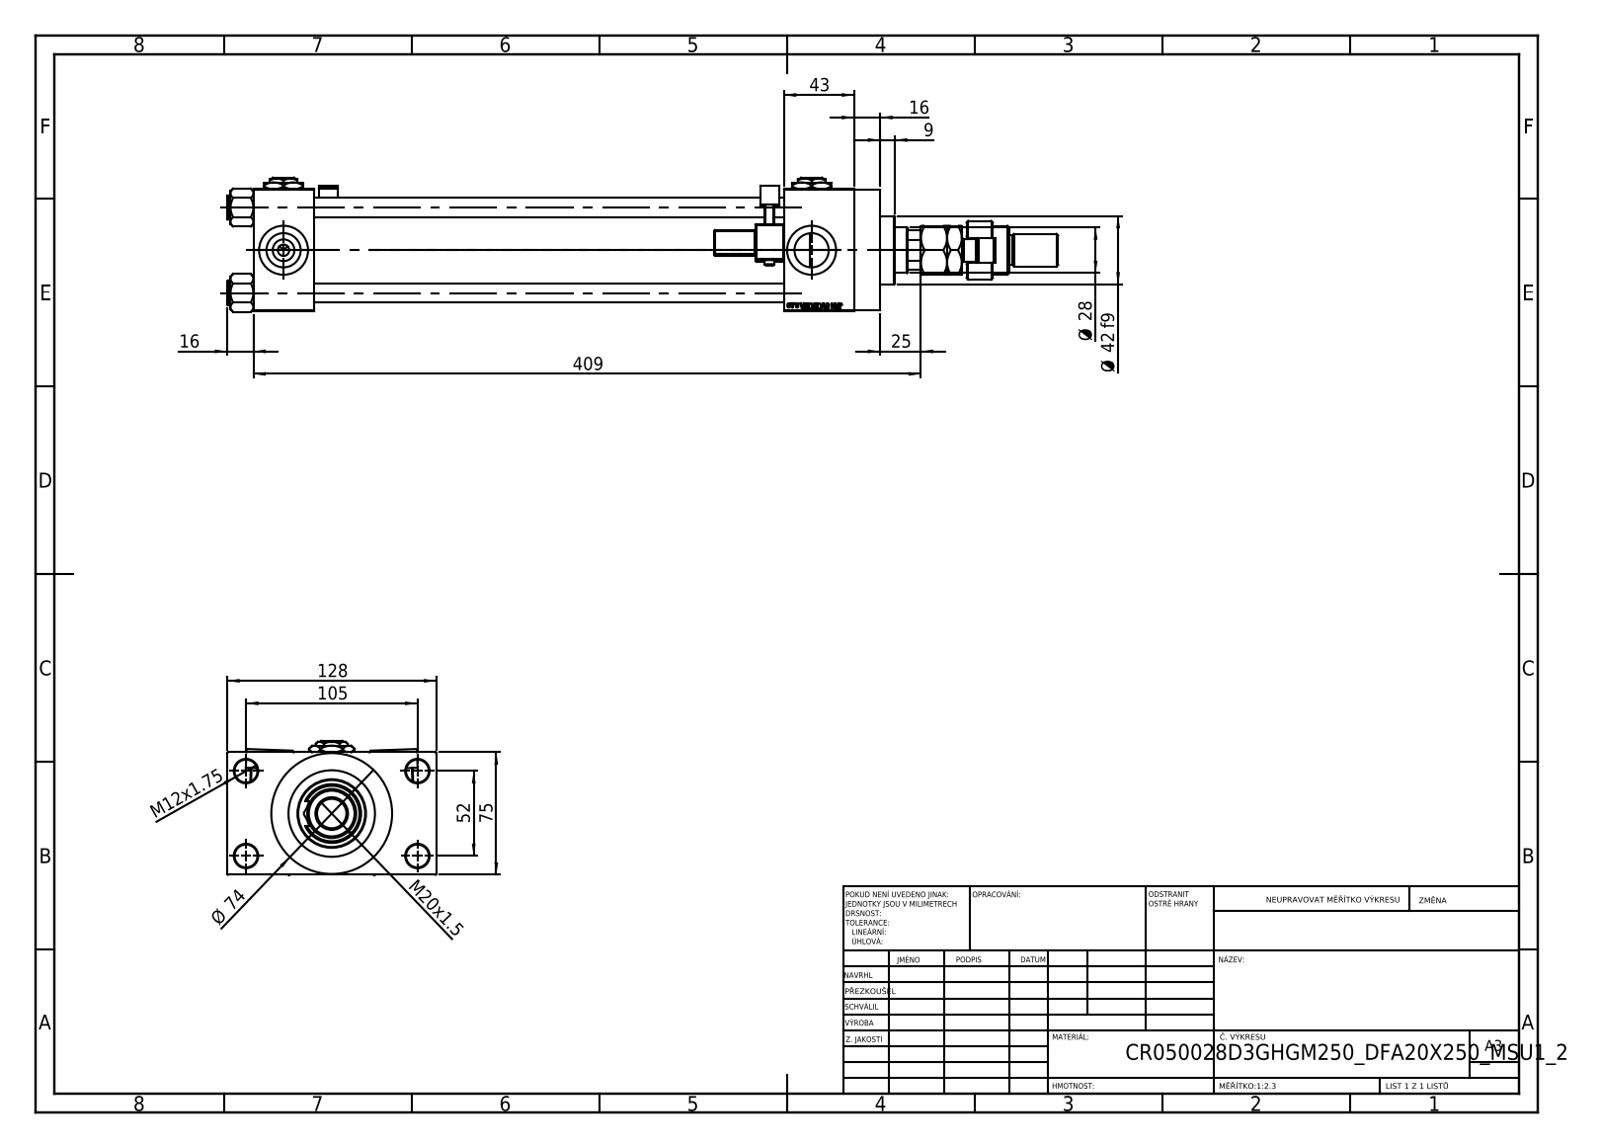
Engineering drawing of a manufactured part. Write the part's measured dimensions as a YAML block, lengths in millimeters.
part_name: "V215CR_MSU; FEMALE_PART_FOR_DFA; V215_VC_A; V215CR_D_Body (+5 more)"
step_written_by: "SolidWorks 2019 (CONFIG_CONTROL_DESIGN)"
units: millimeters
bodies: {solids: 17, faces: 1443, planar: 631, cylindrical: 172, other: 640}
overall_size: [509, 128, 82.27]
volume: 1252000
surface_area: 331861
round_holes:
  - {diameter: 12, count: 4}
  - {diameter: 14, count: 4}
  - {diameter: 20.96, count: 4}
  - {diameter: 30, count: 4}
  - {diameter: 7, count: 3}
  - {diameter: 18.5, count: 1}
  - {diameter: 28, count: 1}
  - {diameter: 31, count: 1}
  - {diameter: 41, count: 1}
  - {diameter: 50, count: 1}
  - {diameter: 53, count: 1}
round_bosses_or_shafts:
  - {diameter: 15, count: 4}
  - {diameter: 6, count: 2}
  - {diameter: 74, count: 1}
  - {diameter: 56, count: 1}
  - {diameter: 42, count: 1}
  - {diameter: 36, count: 1}
  - {diameter: 30, count: 1}
  - {diameter: 22, count: 1}
partial_cylinders:
  - {radius: 0.5, count: 48}
  - {radius: 1, count: 2}
  - {radius: 2.5, count: 2}
  - {radius: 4, count: 2}
  - {radius: 7.5, count: 1}
  - {radius: 12, count: 1}
  - {radius: 13.5, count: 1}
face_to_face_distances: [75, 288, 37, 325, 26.5, 101.5, 43, 368, 331, 16]
hole_center_spacings: [26.35, 36.98, 52.3, 58.43, 58.59, 78.65, 94.37, 52]
